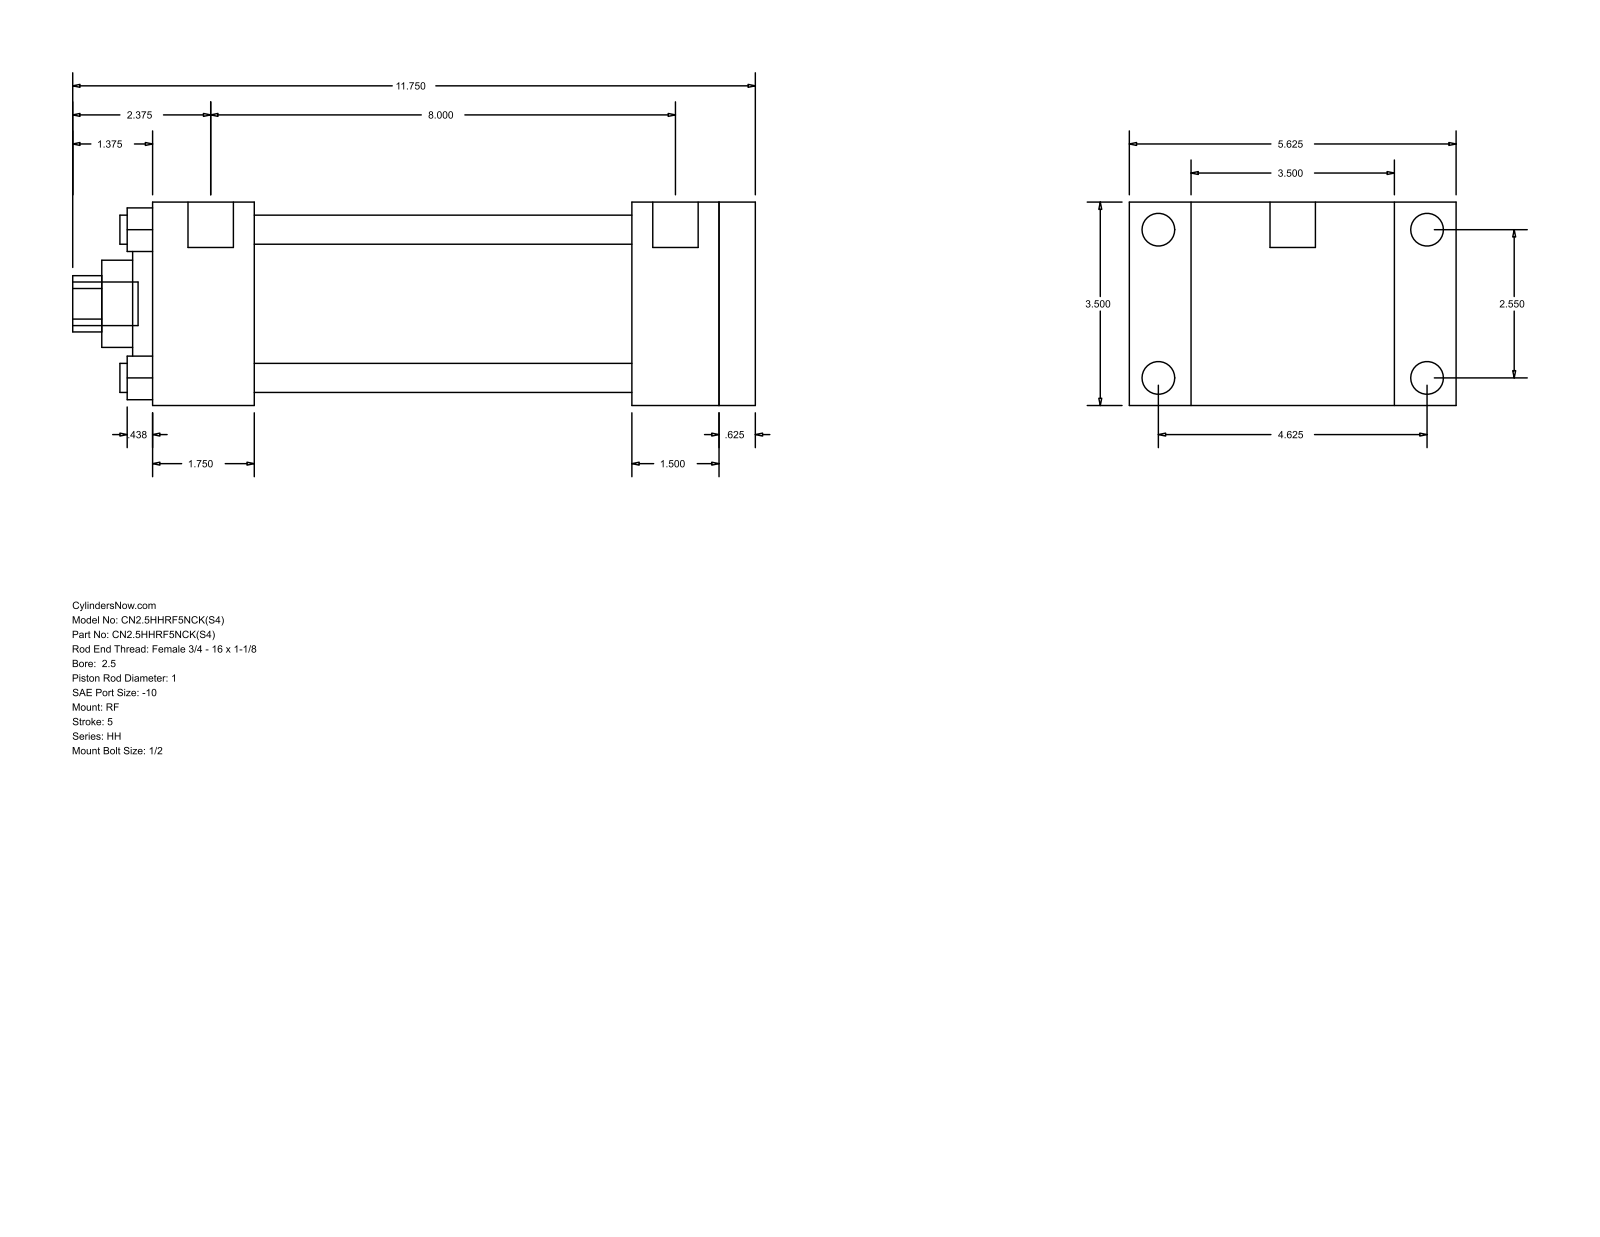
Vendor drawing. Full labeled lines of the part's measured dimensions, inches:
Part name (STEP PRODUCT): HH_RF__0250_1
STEP written by: GSSL Pune (CONFIG_CONTROL_DESIGN)
Units: inches
Bodies: 0 solids, 94 faces (65 planar, 29 cylindrical, 0 other)
Overall size (bounding box): 11.75 × 5.625 × 3.5
Round holes (diameter × count): ⌀0.5 ×4, ⌀1 ×1, ⌀1.5 ×1, ⌀2.375 ×1, ⌀2.875 ×1
Round bosses / shafts (diameter × count): ⌀0.563 ×4, ⌀0.219 ×4, ⌀0.781 ×2, ⌀0.75 ×1
Partial cylindrical surfaces — rounded edges, fillets, slot ends (radius × count): R0.484 ×1
Main face-to-face distances: 3.5, 0.625, 9.75, 10.375, 1.75, 8, 8.625, 8.25, 6.5, 1.5
Hole centre spacings: 1.803, 2.55, 3.606
